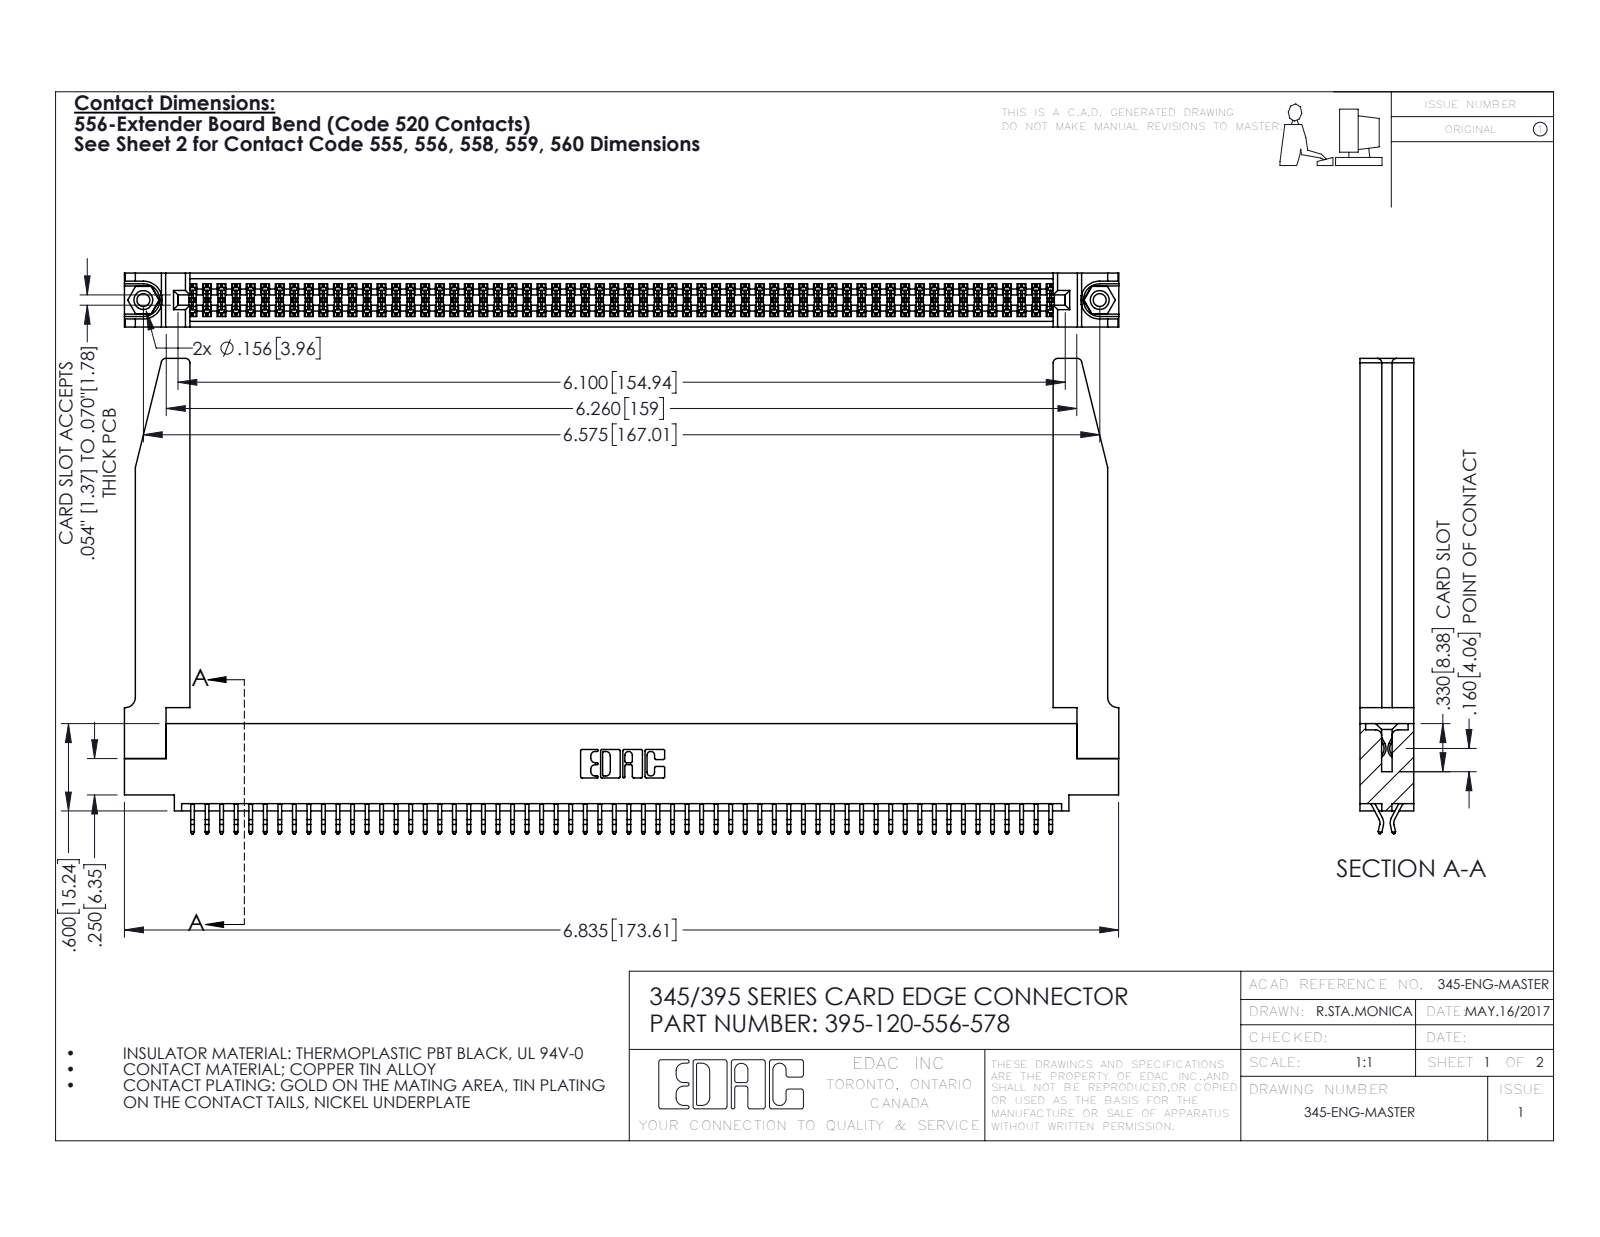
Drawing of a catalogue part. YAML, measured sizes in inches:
part_name: "345 Part_0.110 Offset - 0.156 Dia-TH; 345-292-001_556 Tail; 345-250-001_345-250-001-102; 395-120-556-578 (+1 more)"
step_written_by: "SolidWorks 2016 (CONFIG_CONTROL_DESIGN)"
units: inches
bodies: {solids: 125, faces: 7084, planar: 4666, cylindrical: 2366, other: 52}
overall_size: [6.836, 3.267, 0.37]
volume: 1.509
surface_area: 49.97
round_holes:
  - {diameter: 0.089, count: 2}
  - {diameter: 0.125, count: 2}
  - {diameter: 0.156, count: 2}
  - {diameter: 0.064, count: 1}
round_bosses_or_shafts:
  - {diameter: 0.155, count: 2}
partial_cylinders:
  - {radius: 0.006, count: 180}
  - {radius: 0.01, count: 22}
  - {radius: 0.03, count: 8}
  - {radius: 0.007, count: 6}
  - {radius: 0.031, count: 6}
  - {radius: 0.026, count: 3}
  - {radius: 0.01, count: 2}
  - {radius: 0.014, count: 2}
face_to_face_distances: [0.072, 0.37, 0.298, 0.025, 0.098, 0.272, 0.2, 0.225, 0.175, 0.148]
hole_center_spacings: [0.27, 6.339, 6.575]
